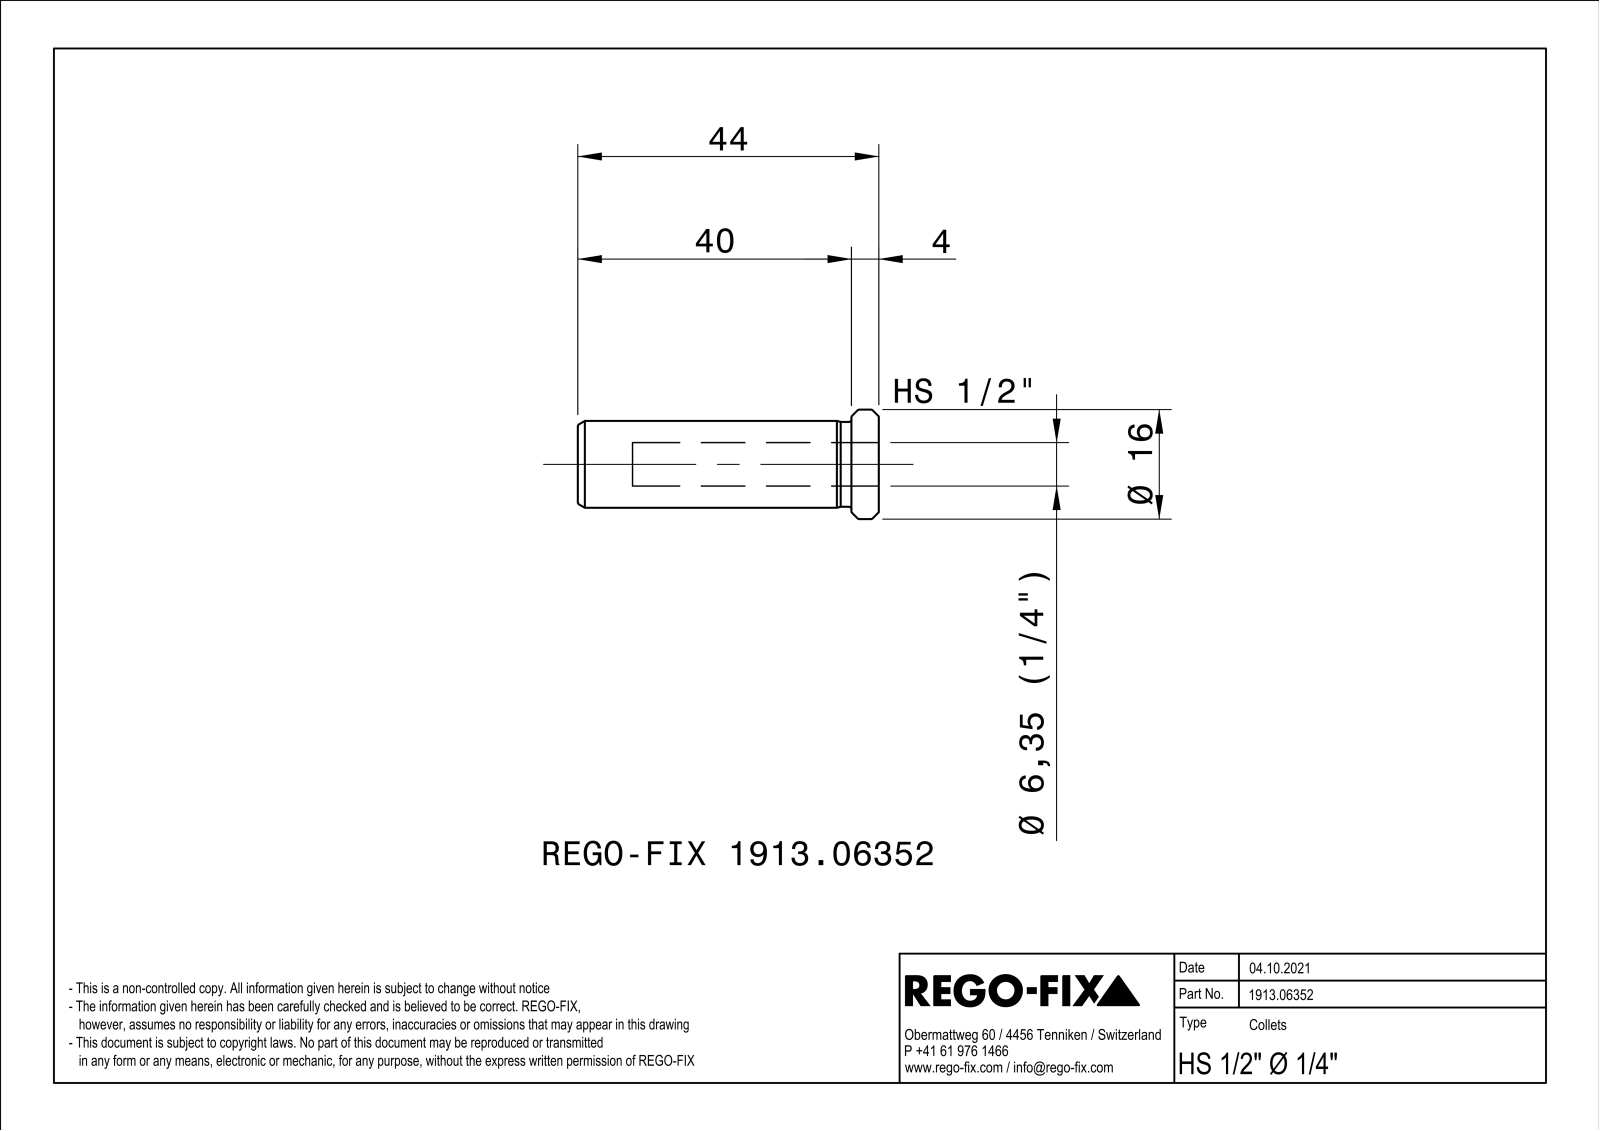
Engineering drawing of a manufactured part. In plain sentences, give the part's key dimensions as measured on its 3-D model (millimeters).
The part is named "NOCUT". Its 3-D file was written by "SIEMENS PLM Software Solid Edge ST10 (AUTOMOTIVE_DESIGN)". It is 1 solid with 70 faces: 22 planar, 11 cylindrical and 37 other. Overall it measures 44 by 15.98 by 15.98 millimeters. Its volume is 3 987 cubic millimeters and its surface area 3 578 square millimeters. Round holes: 1 of diameter 6.35, 1 of diameter 7.5. Round bosses or shafts: 1 of diameter 16, 1 of diameter 12.7, 1 of diameter 12.4. The main face-to-face distances are 0.8, 44, 4, 40.
